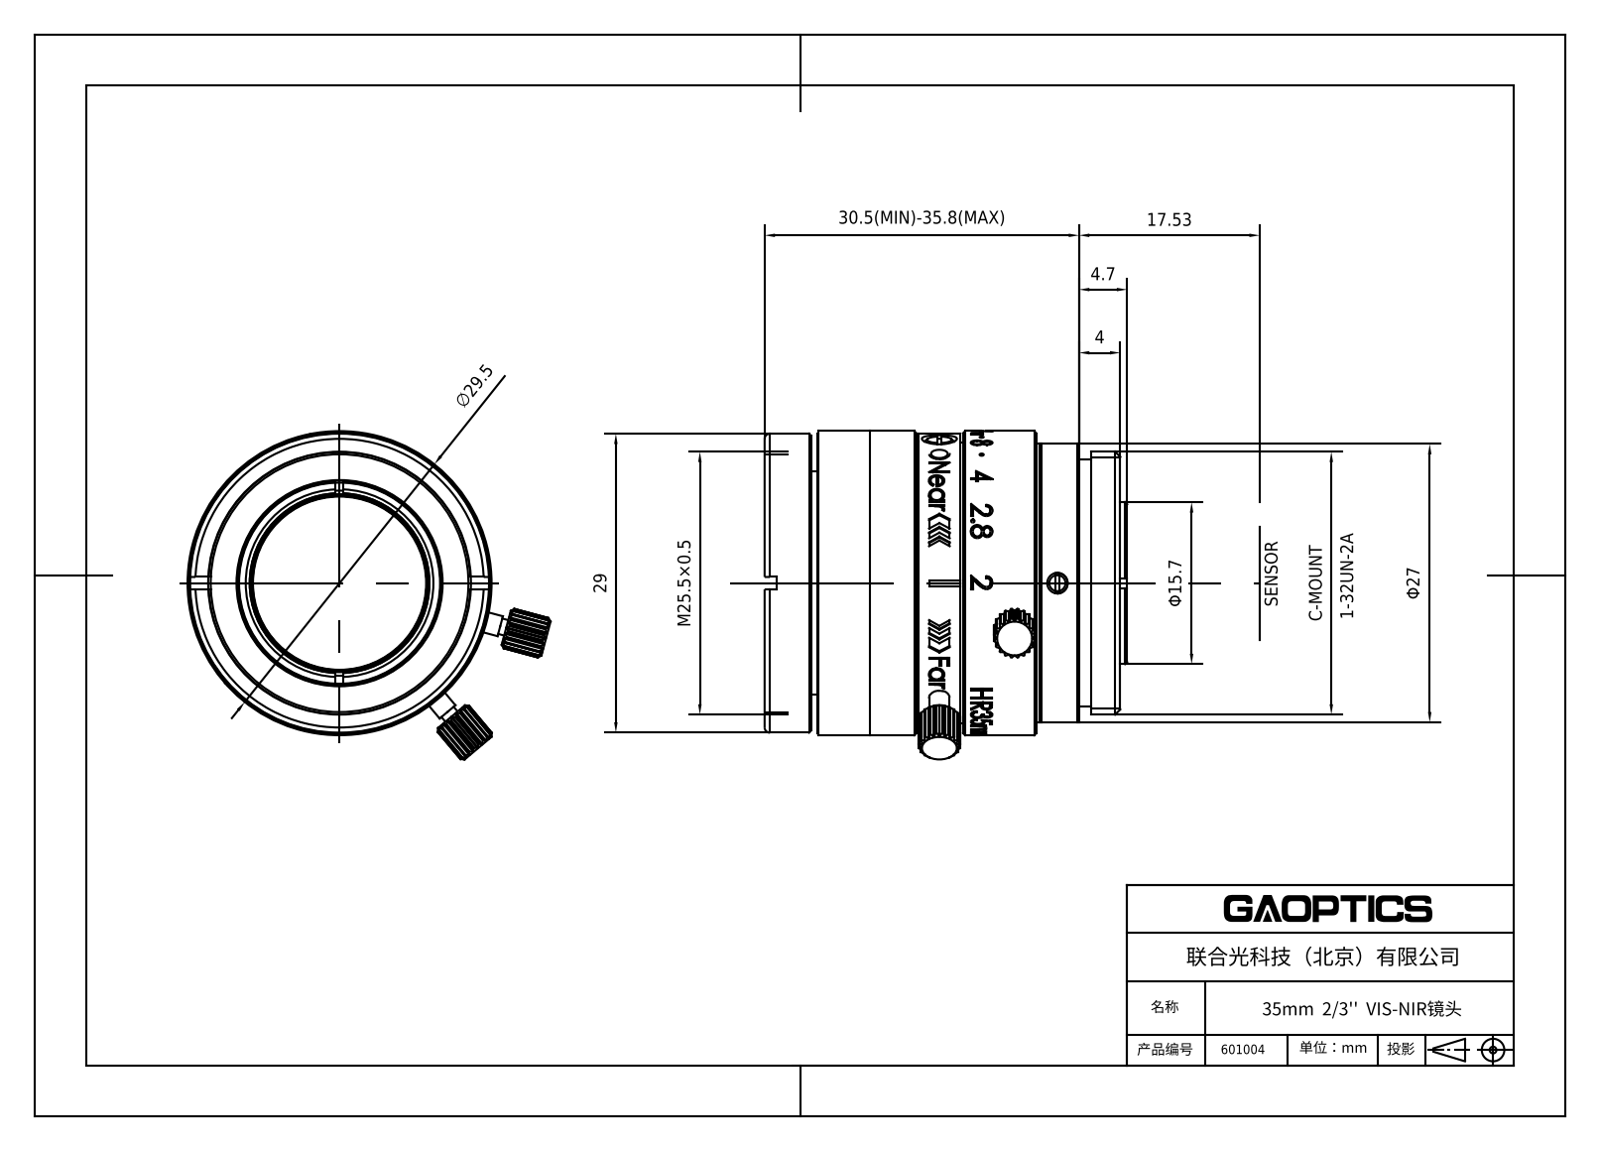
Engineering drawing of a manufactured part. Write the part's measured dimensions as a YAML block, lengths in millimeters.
part_name: "601004"
step_written_by: "SolidWorks 2019 (CONFIG_CONTROL_DESIGN)"
units: millimeters
bodies: {solids: 2, faces: 621, planar: 0, cylindrical: 0, other: 621}
overall_size: [34.34, 34.31, 29.5]
volume: 18398
surface_area: 7795
